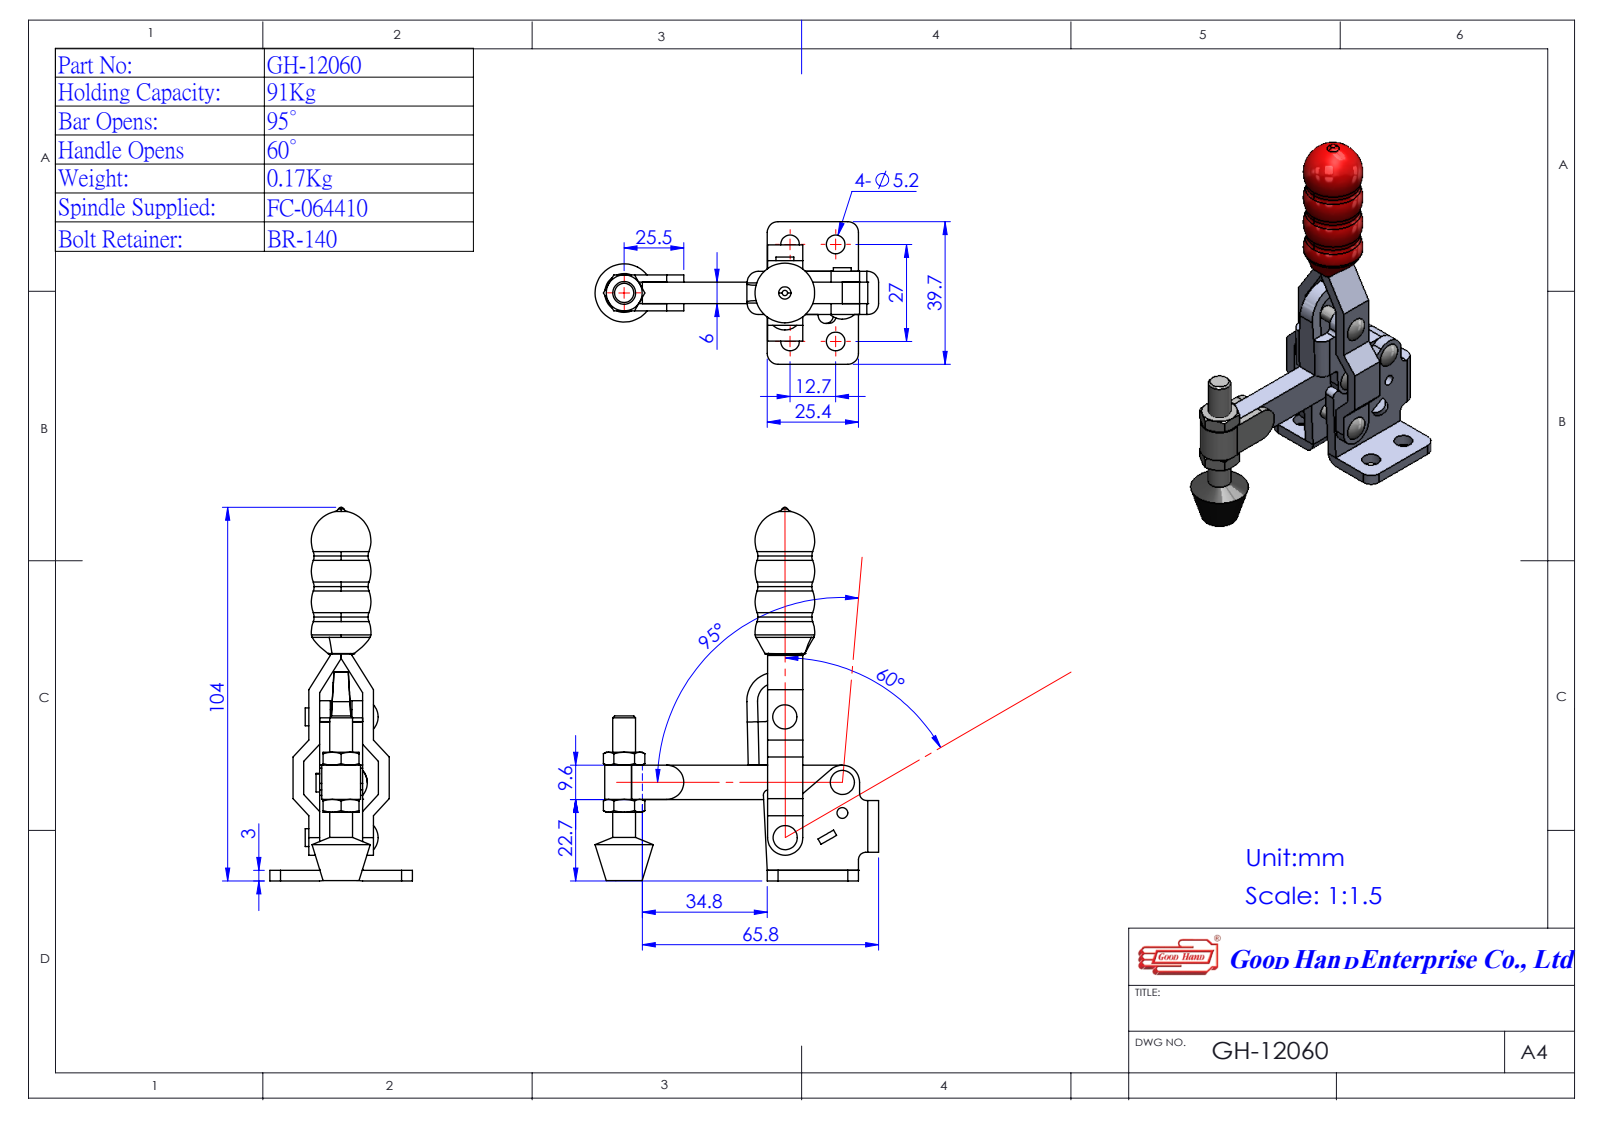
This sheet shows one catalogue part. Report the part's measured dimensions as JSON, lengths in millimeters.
{"part_name": "Group1_112055U01; GH-12060(簡化); 11206008_00-1^GH-12060(簡化); Group3^GH-12060(簡化) (+2 more)", "step_written_by": "SolidWorks 2016 (AUTOMOTIVE_DESIGN)", "units": "millimeters", "bodies": {"solids": 5, "faces": 283, "planar": 118, "cylindrical": 107, "other": 58}, "overall_size": [104.11, 77.59, 39.7], "volume_mm3": 27737, "surface_area_mm2": 18038, "round_holes": [[3, 4], [5.2, 4]], "round_bosses_or_shafts": [[5, 4], [6.35, 1]], "partial_cylinders_radius": [[3, 4], [1, 2], [2, 2], [2.02, 2], [4.5, 2], [5, 2], [1.5, 1], [2.5, 1]], "face_to_face_distances": [3, 9, 6, 12, 19.4, 4.4, 7.4, 16.4, 15, 9.8], "hole_center_spacings": [12.7, 27, 29.84, 15.23, 15.38, 18.4, 22.11, 24.42]}
